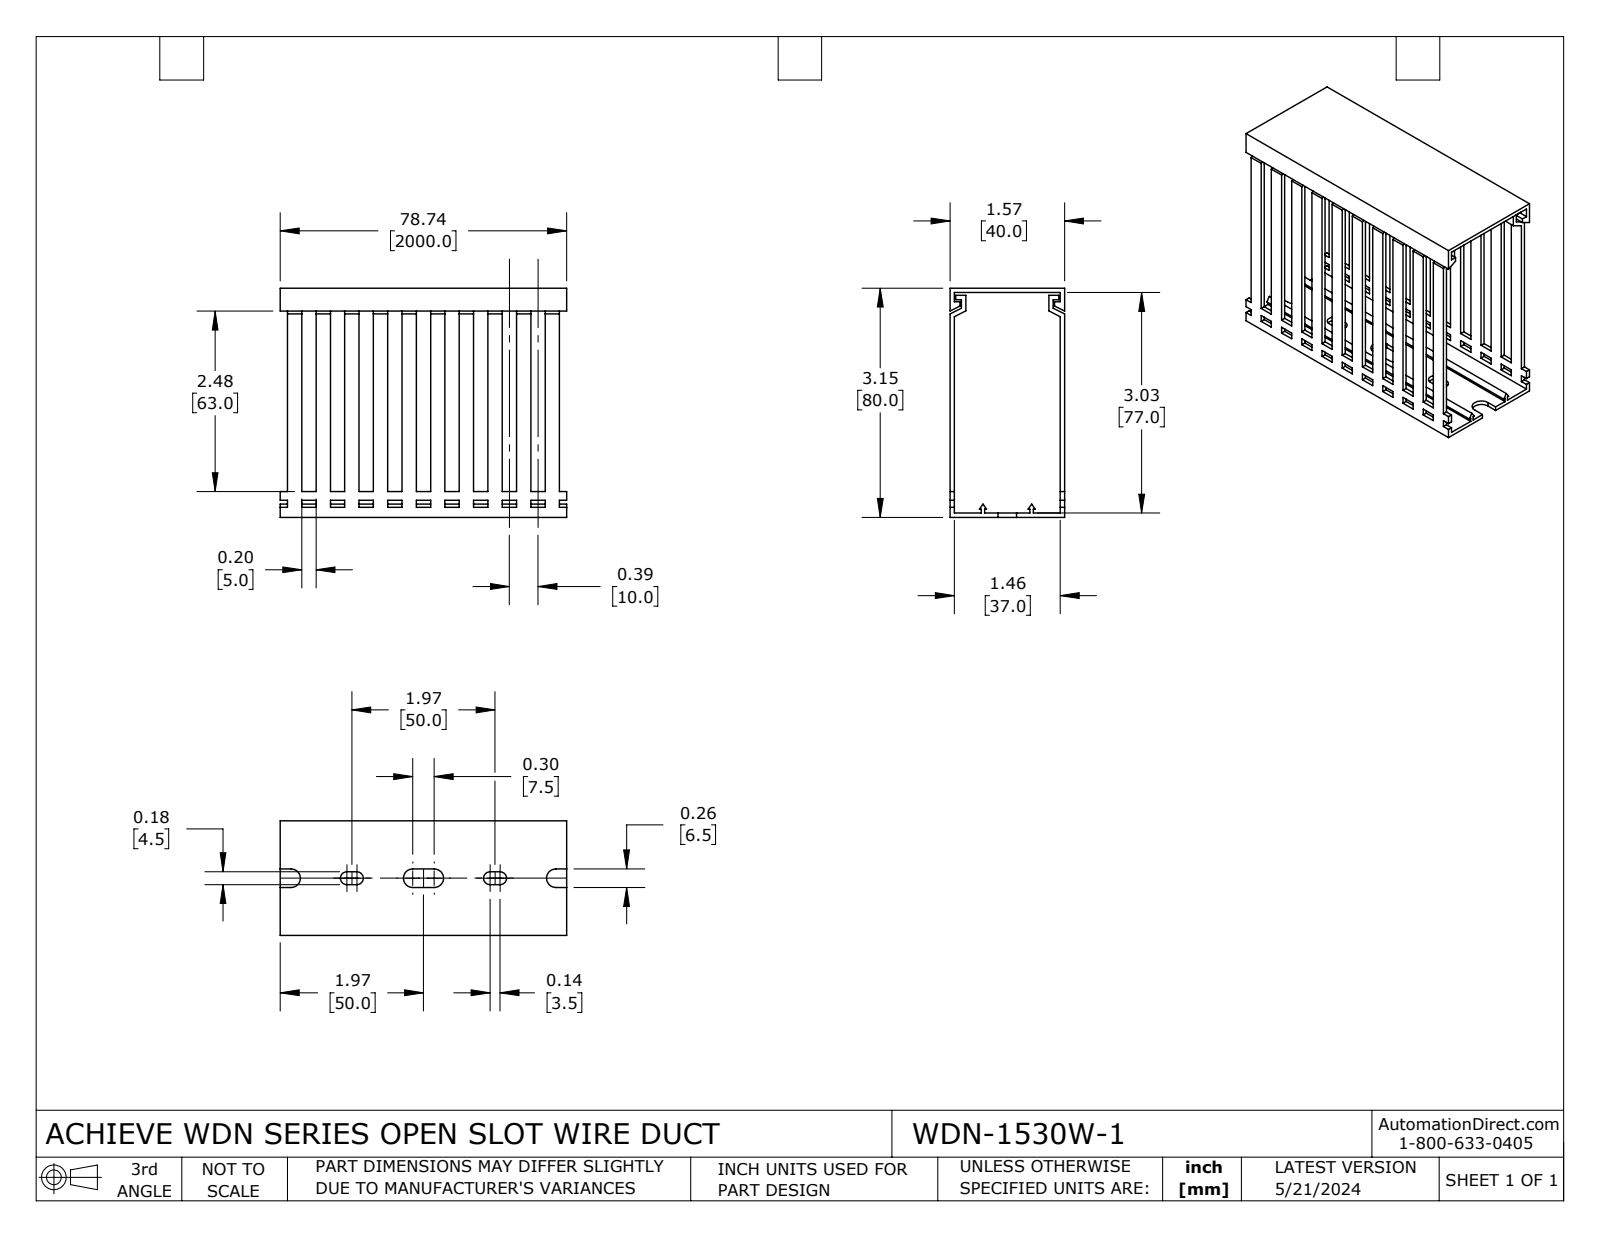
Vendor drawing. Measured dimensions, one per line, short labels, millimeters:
name: WDN-1530W-1
written by: SolidWorks 2023 (CONFIG_CONTROL_DESIGN)
unit: mm
bodies: 2 solids, 350 faces (338 planar, 12 cylindrical, 0 other)
size: 100 × 80 × 40
volume: 27 890 mm³; area: 43 120 mm²
rounds: 4× R2.3, 4× R3.3
face distances: 1.5, 38.5, 40, 78.5, 80, 5, 10, 37, 15, 20
